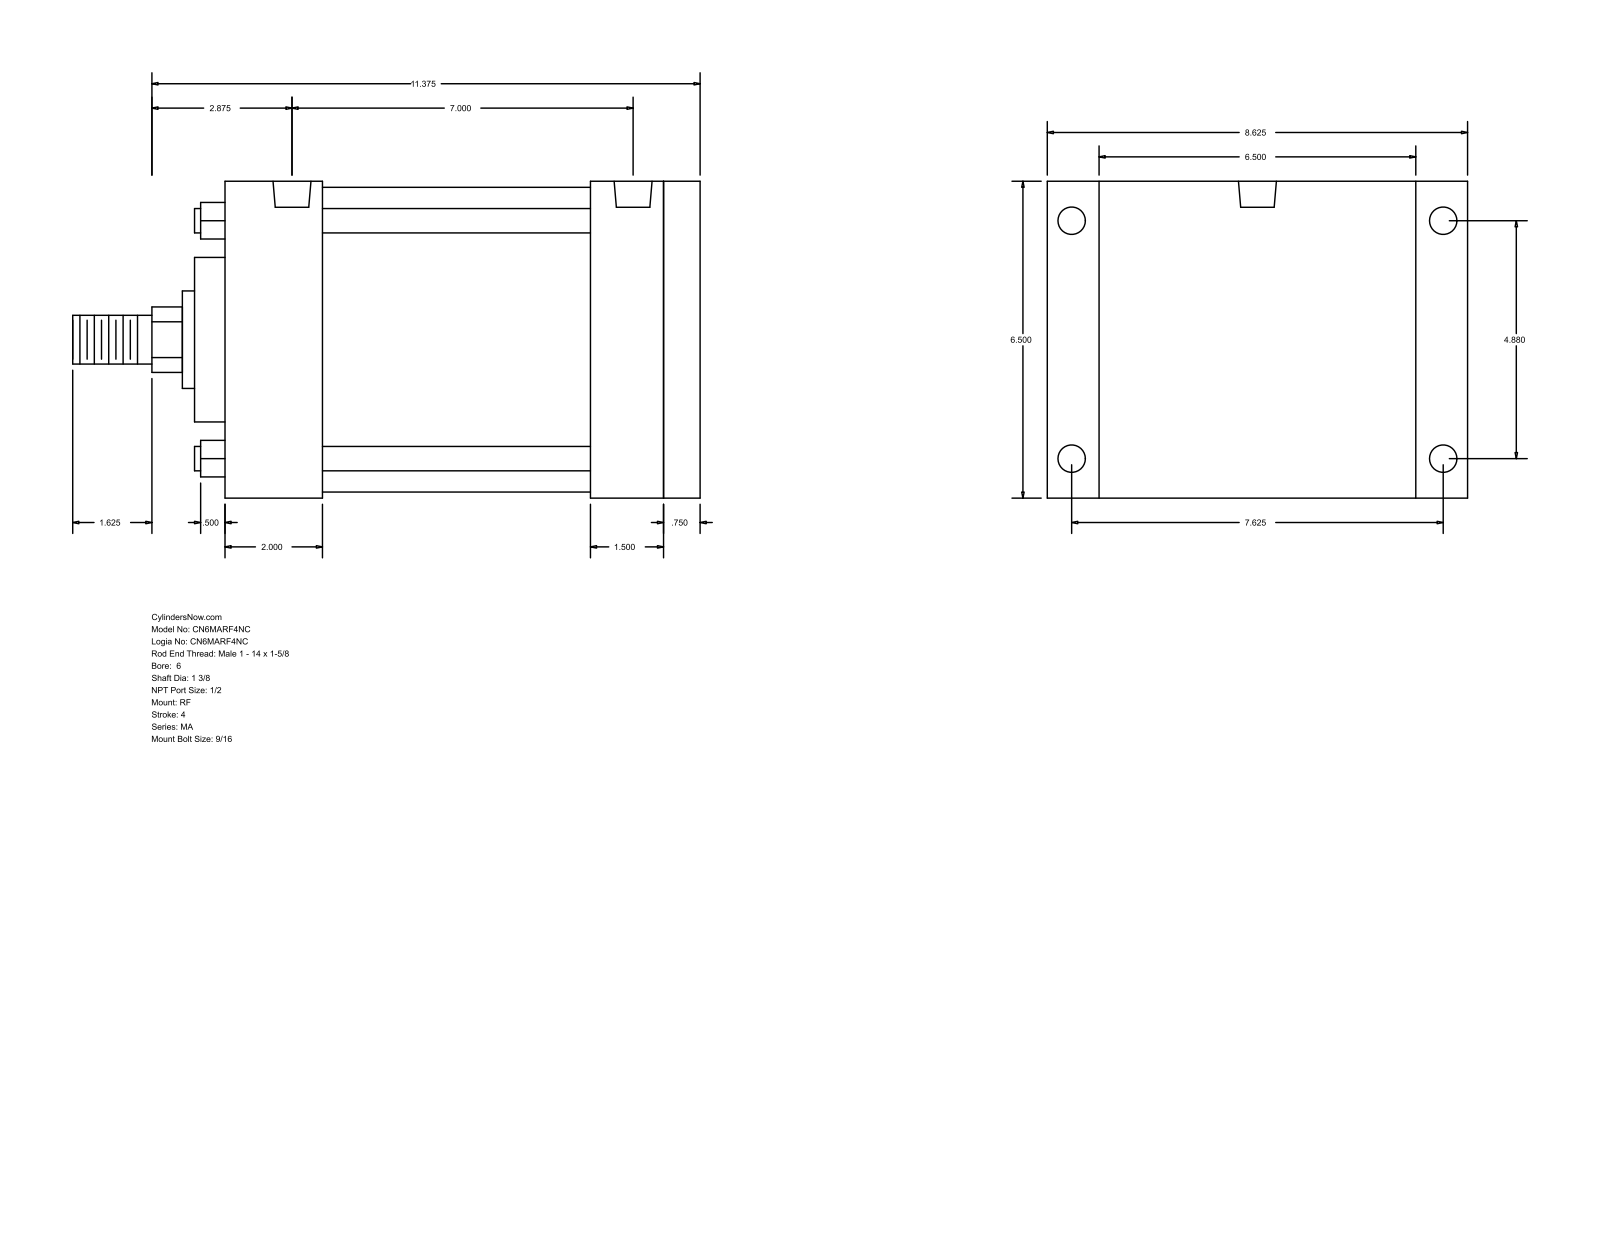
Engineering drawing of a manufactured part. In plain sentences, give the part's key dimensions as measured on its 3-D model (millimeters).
The part is named "MA_RF__0600_1.375". Its 3-D file was written by "GSSL Pune (CONFIG_CONTROL_DESIGN)". It is 0 solids with 94 faces: 65 planar, 29 cylindrical and 0 other. Overall it measures 330.2 by 219.07 by 165.1 millimeters. Round holes: 4 of diameter 14.29, 4 of diameter 17.46, 2 of diameter 19.77. Round bosses or shafts: 4 of diameter 12.7, 1 of diameter 158.75, 1 of diameter 85.72, 1 of diameter 50.8, 1 of diameter 34.92, 1 of diameter 25.4. Partial cylindrical surfaces (rounded edges, fillets, slot ends): 1 of radius 17.06. The main face-to-face distances are 165.1, 250.83, 19.05, 231.78, 57.15, 38.1, 50.8, 180.98, 200.03, 193.68. The hole center spacings are 123.96, 180.97, 193.68, 229.95, 3.18, 177.79.
